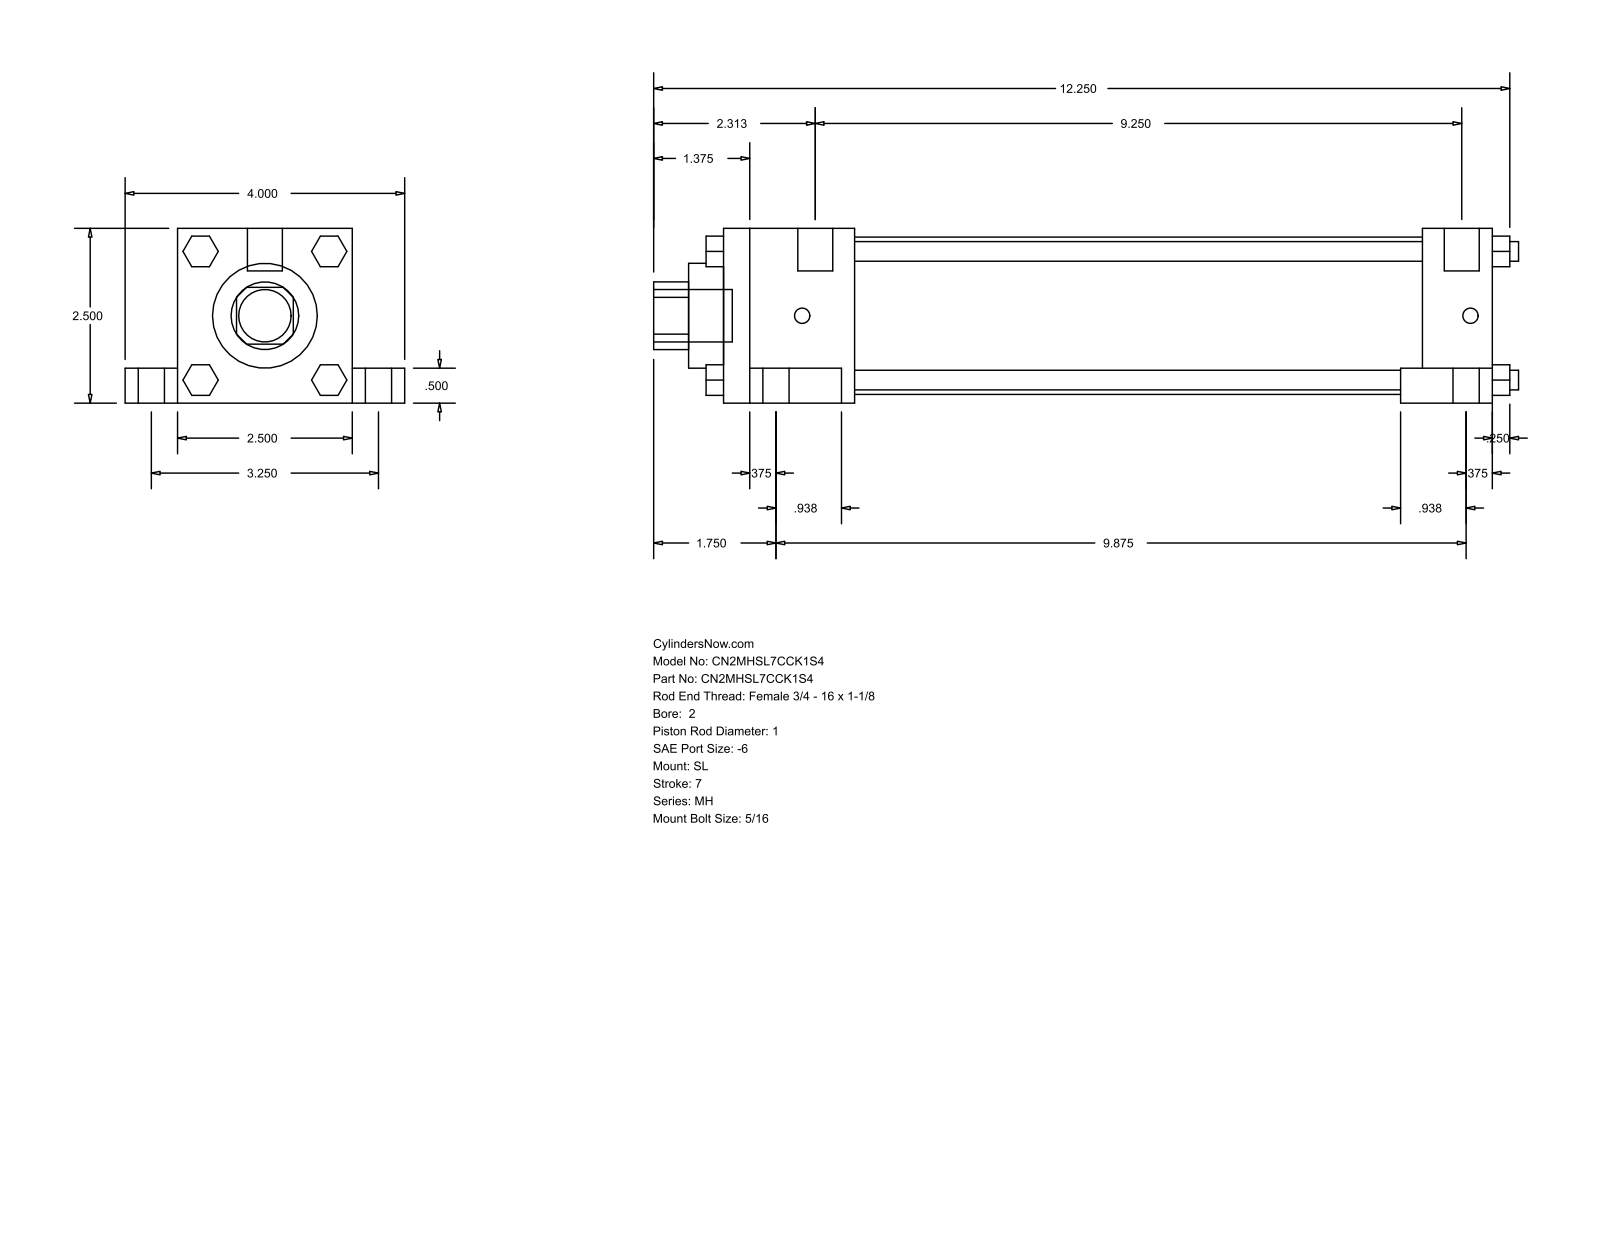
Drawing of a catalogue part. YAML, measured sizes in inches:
part_name: "MH_SL__0200_1"
step_written_by: "GSSL Pune (CONFIG_CONTROL_DESIGN)"
units: inches
bodies: {solids: 0, faces: 148, planar: 112, cylindrical: 36, other: 0}
overall_size: [12.375, 4, 2.5]
round_holes:
  - {diameter: 1, count: 1}
  - {diameter: 1.5, count: 1}
  - {diameter: 2.25, count: 1}
round_bosses_or_shafts:
  - {diameter: 0.625, count: 4}
  - {diameter: 0.375, count: 4}
  - {diameter: 0.281, count: 4}
  - {diameter: 0.219, count: 4}
  - {diameter: 0.5, count: 2}
  - {diameter: 0.75, count: 1}
partial_cylinders:
  - {radius: 0.484, count: 1}
face_to_face_distances: [2.5, 11, 0.5, 0.75, 2, 3.25, 0.375, 1, 10, 1.875]
